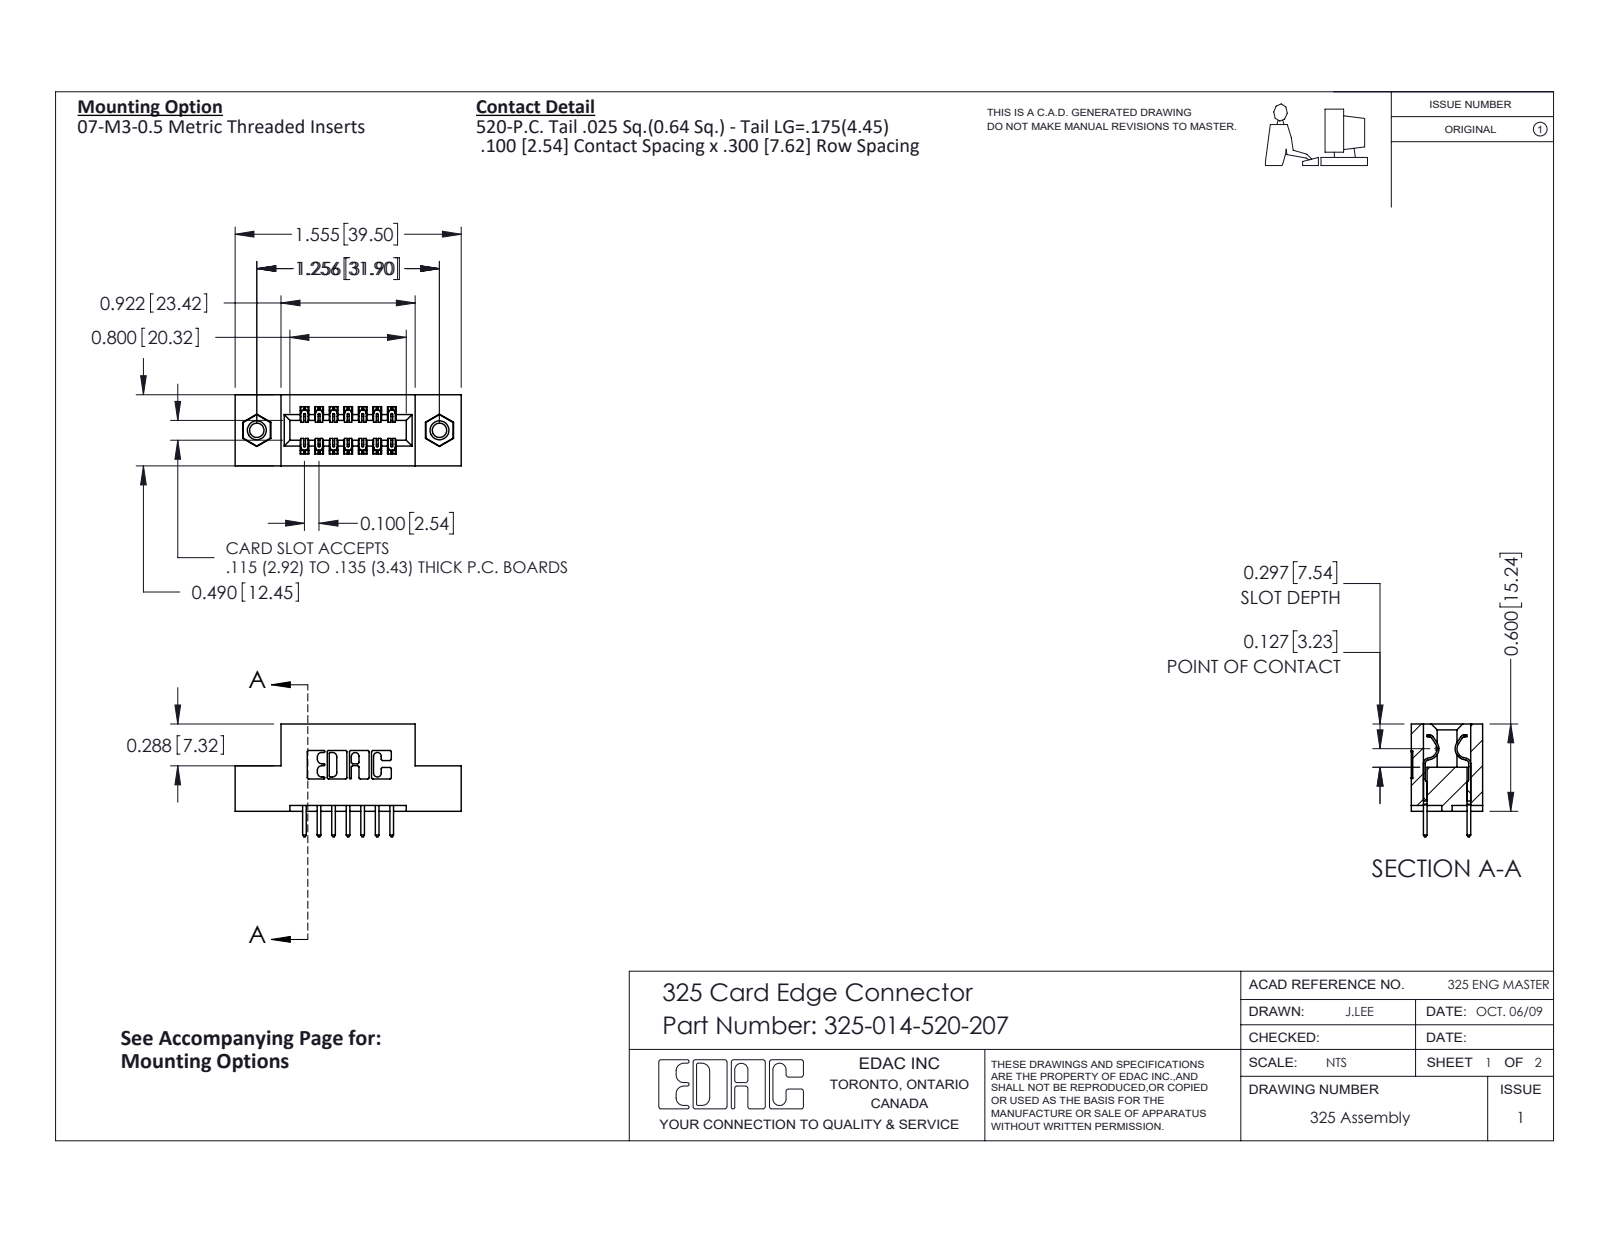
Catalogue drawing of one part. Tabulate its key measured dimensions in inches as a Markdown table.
| quantity | value |
| --- | --- |
| part name | 345-250-001_345-250-005-103; 325 Part_TI; 325-292-001_325-293-120; 325-014-520-207 |
| STEP written by | SolidWorks 2016 (CONFIG_CONTROL_DESIGN) |
| units | inches |
| bodies | 17 solids, 902 faces (606 planar, 280 cylindrical, 16 other) |
| overall size | 1.555 × 0.775 × 0.49 |
| volume | 0.291 in³ |
| surface area | 7.658 in² |
| round holes (diameter × count) | 0.098 × 2, 0.125 × 2, 0.16 × 2 |
| round bosses / shafts (diameter × count) | 0.155 × 2 |
| partial cylindrical surfaces (radius × count) | 0.01 × 22, 0.006 × 21, 0.01 × 14, 0.007 × 6, 0.031 × 6, 0.026 × 3, 0.014 × 2, 0.022 × 2 |
| main face-to-face distances | 0.3, 0.1, 0.083, 0.407, 0.2, 0.04, 0.49, 0.06, 0.16, 0.4 |
| hole center spacings | 1.256 |
